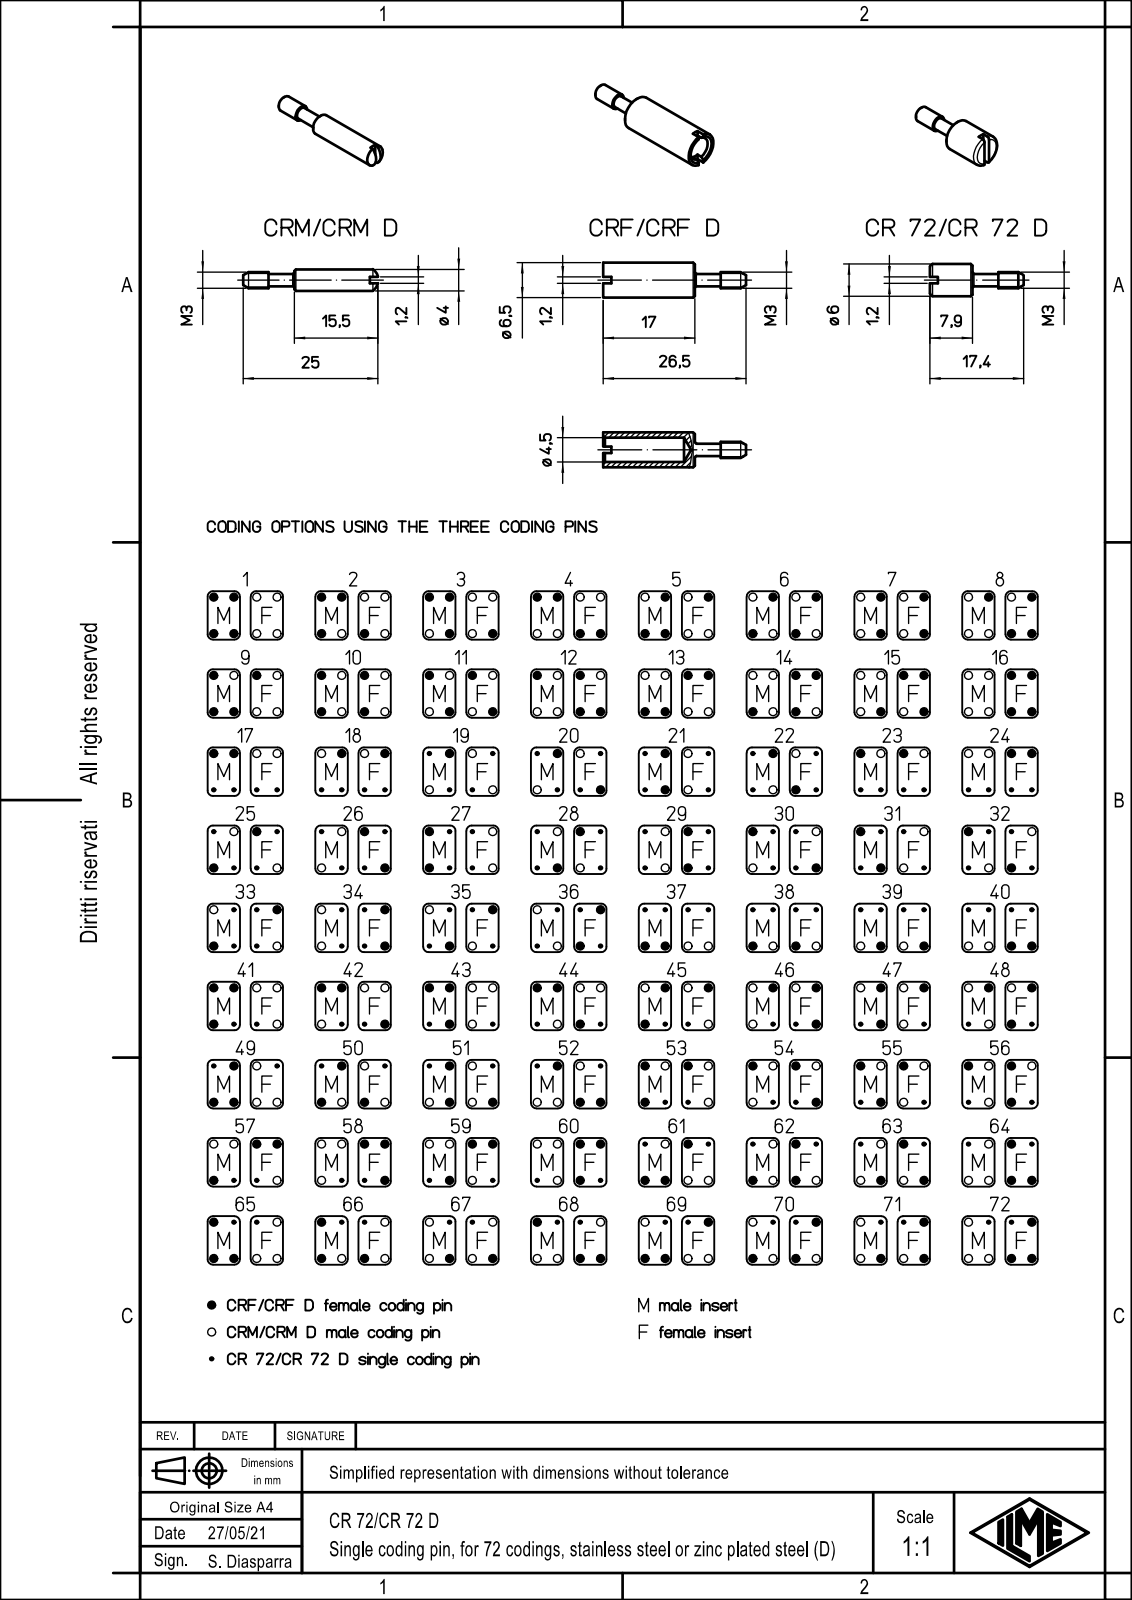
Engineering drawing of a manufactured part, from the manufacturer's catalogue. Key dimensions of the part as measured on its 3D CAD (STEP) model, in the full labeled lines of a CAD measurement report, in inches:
Part name (STEP PRODUCT): CR_72
STEP written by: Creo Elements/Direct Modeling 17.0D 15-Jul-2011 (C) Parametric Technology GmbH (AUTOMOTIVE_DESIGN)
Units: inches
Bodies: 1 solid, 22 faces (8 planar, 6 cylindrical, 8 other)
Overall size (bounding box): 0.685 × 0.236 × 0.236
Volume: 0.016 in³ · Surface area: 0.451 in²
Round bosses / shafts (diameter × count): ⌀0.236 ×1, ⌀0.118 ×1, ⌀0.091 ×1
Main face-to-face distances: 0.311, 0.047, 0.252, 0.059, 0.197, 0.448, 0.507, 0.177, 0.374, 0.626
